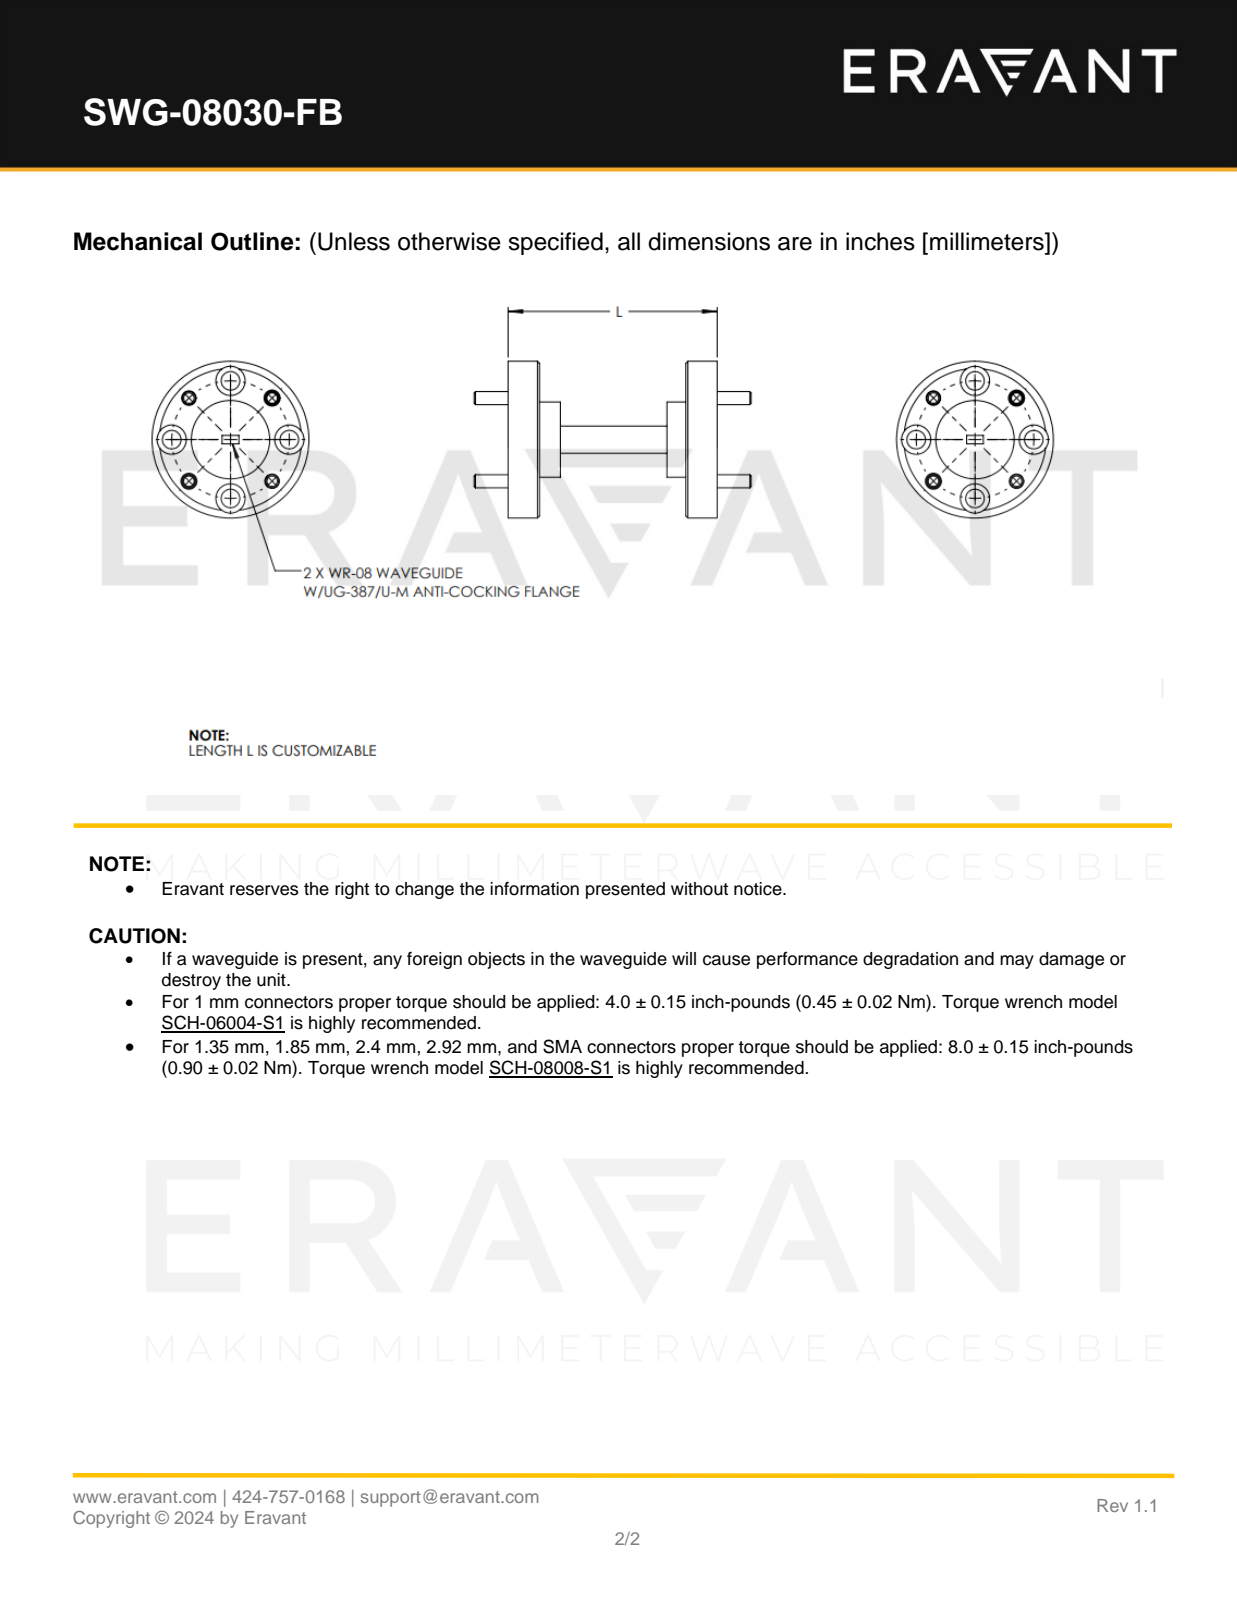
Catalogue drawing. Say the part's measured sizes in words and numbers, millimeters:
The part is named "SWG-08030-FB-A-P". Its 3-D file was written by "SolidWorks 2021 (CONFIG_CONTROL_DESIGN)". It is 5 solids with 152 faces: 40 planar, 76 cylindrical and 36 other. Overall it measures 84.5 by 19.1 by 19.1 millimeters. Its volume is 3 130 cubic millimeters and its surface area 3 205 square millimeters. Round holes: 4 of diameter 1.5, 4 of diameter 1.7, 4 of diameter 2.3, 4 of diameter 3.6, 1 of diameter 17.3. Round bosses or shafts: 4 of diameter 1.6, 1 of diameter 19.1, 1 of diameter 9.5, 1 of diameter 9.1. The main face-to-face distances are 3.3, 3.8, 72.4, 75.7, 0.5, 3.3, 71.9, 4.6, 68.6, 76.2. The hole center spacings are 5.5, 10.1, 13.2, 7.1, 7.1, 14.3, 10.1, 13.2.
